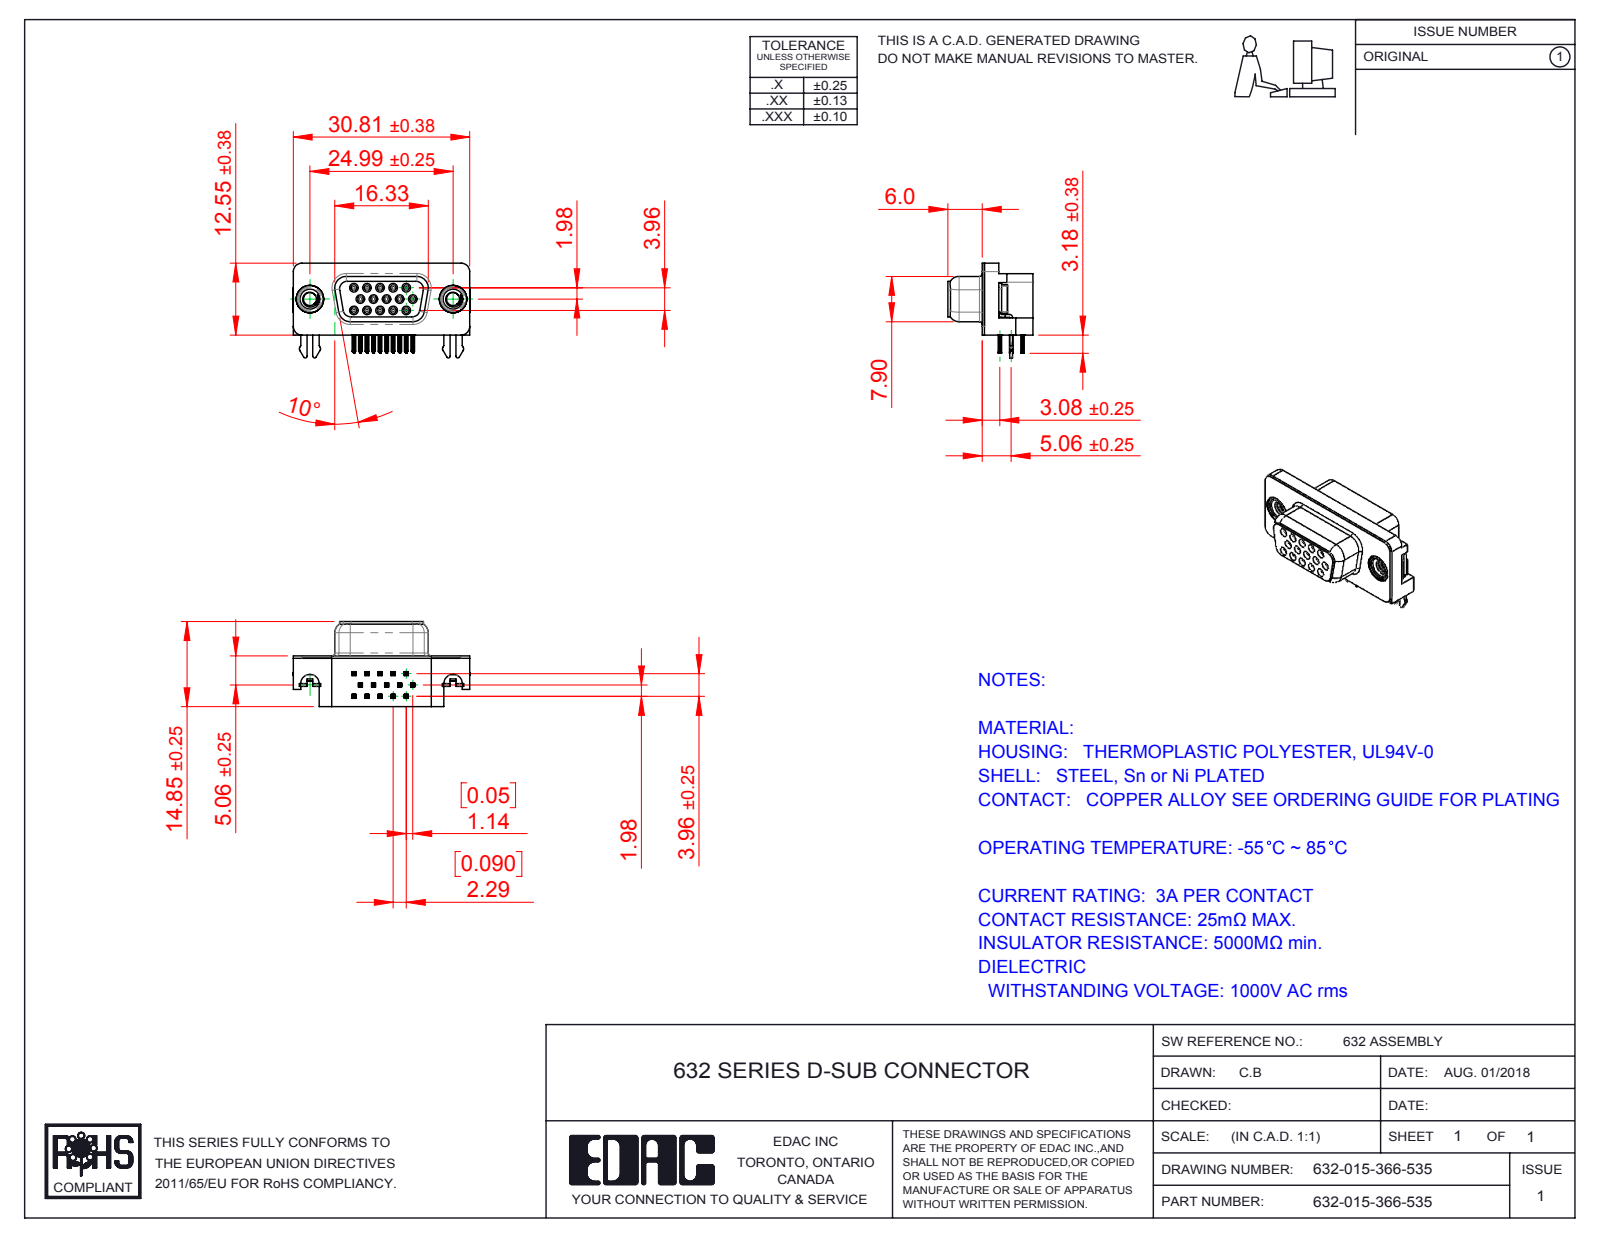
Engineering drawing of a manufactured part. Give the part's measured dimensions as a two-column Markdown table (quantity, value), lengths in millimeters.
| quantity | value |
| --- | --- |
| part name | 632 Contact Top; 632 4-40 Threaded Rivet; 632 M3 Threaded Rivet; 632 Contact Middle (+5 more) |
| STEP written by | SolidWorks 2016 (CONFIG_CONTROL_DESIGN) |
| units | millimeters |
| bodies | 23 solids, 2426 faces (1006 planar, 654 cylindrical, 766 other) |
| overall size | 30.89 × 16.55 × 14.85 |
| volume | 2 996 mm³ |
| surface area | 5 342 mm² |
| round holes (diameter × count) | 0.8 × 15, 0.9 × 15, 2.26 × 2, 2.5 × 2, 4 × 2, 4.8 × 2, 5 × 2 |
| round bosses / shafts (diameter × count) | 1.2 × 15, 4.9 × 2, 4.75 × 2, 3.9 × 2 |
| partial cylindrical surfaces (radius × count) | 0.1 × 120, 0.15 × 60, 0.35 × 30, 0.34 × 15, 1 × 11, 0.28 × 10, 0.5 × 10, 0.25 × 8 |
| main face-to-face distances | 0.4, 8.45, 8.85, 1.98, 2.9, 5.95, 2.5, 6.4, 6.7, 7.05 |
| hole center spacings | 2.28, 2.29, 3.96, 4.57, 6.05, 3.97, 4.58, 6.86 |
